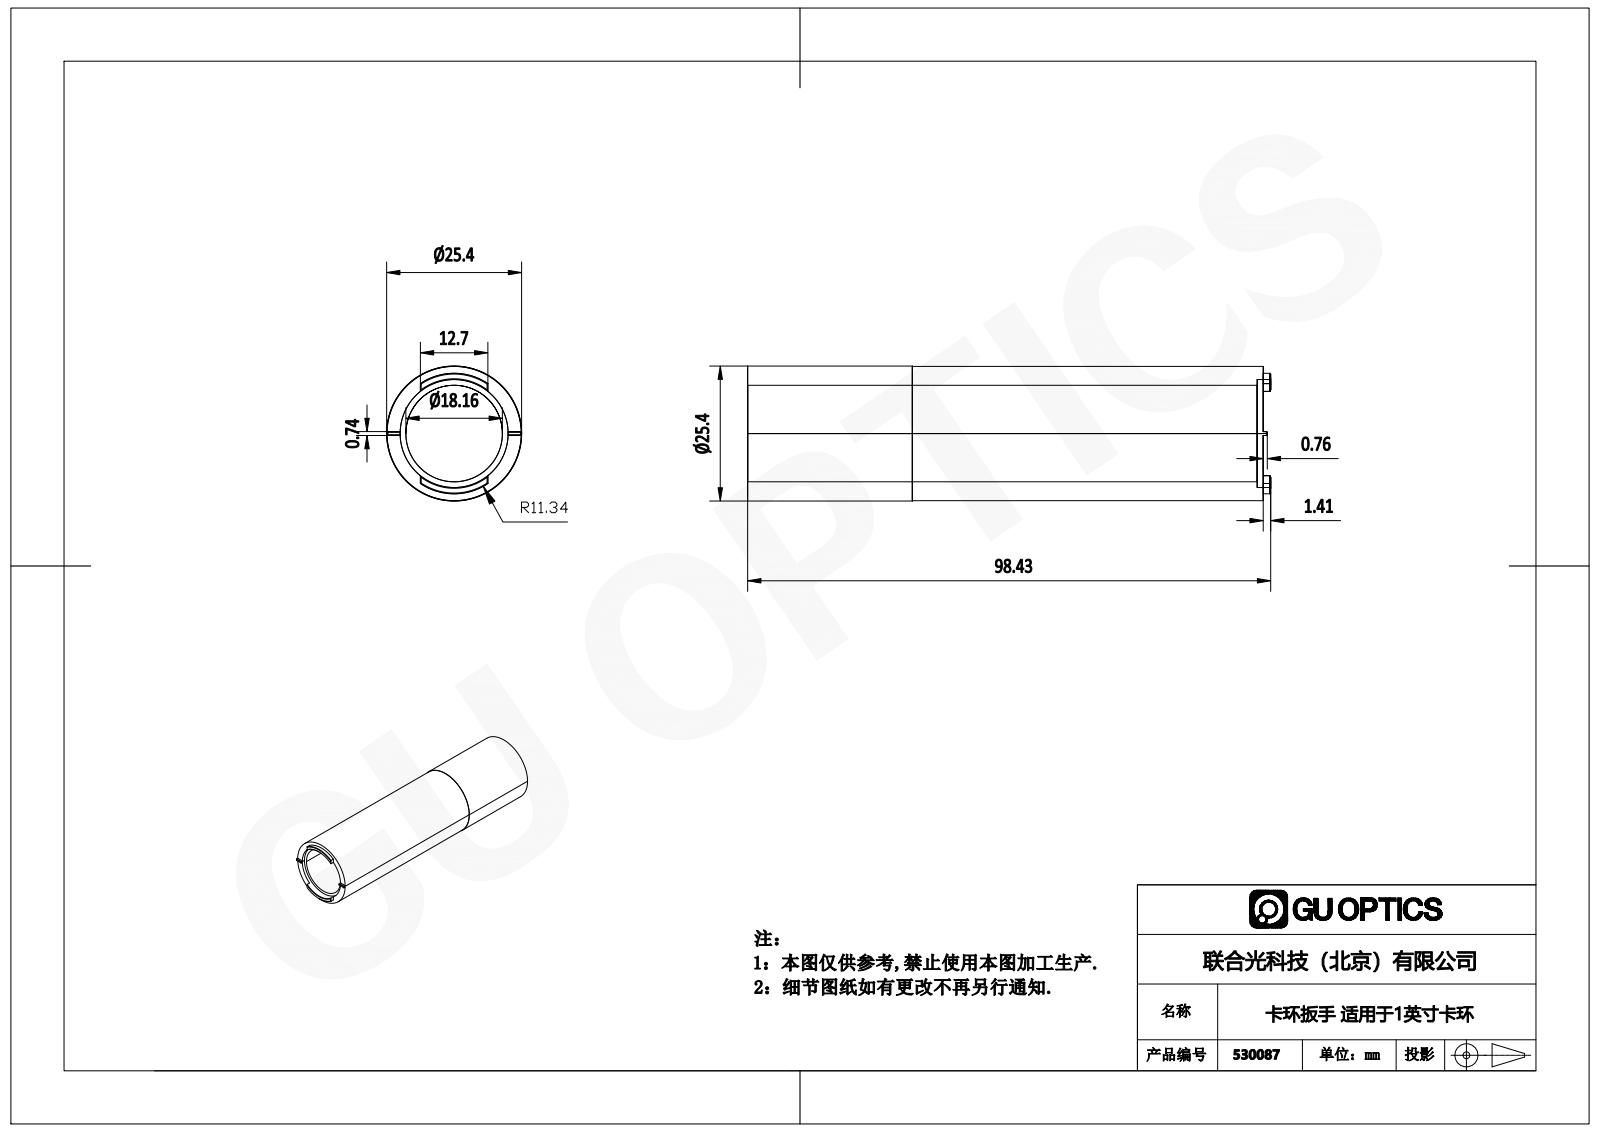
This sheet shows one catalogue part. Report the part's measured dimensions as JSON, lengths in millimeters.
{"part_name": "1.8.2.9_ZFG-K1.0L_卡环扳手，适用于1英寸卡环，长度3.88英寸", "step_written_by": "SolidWorks 2018 (AUTOMOTIVE_DESIGN)", "units": "millimeters", "bodies": {"solids": 0, "faces": 42, "planar": 25, "cylindrical": 10, "other": 7}, "overall_size": [98.43, 25.4, 25.4], "round_holes": [[18.16, 1], [20.32, 1]], "round_bosses_or_shafts": [[25.4, 1], [25.27, 1]], "partial_cylinders_radius": [[11.34, 1]], "face_to_face_distances": [97.03, 95.89, 1.14, 98.43, 2.54, 1.4, 31, 64.89, 66.03, 67.43]}
